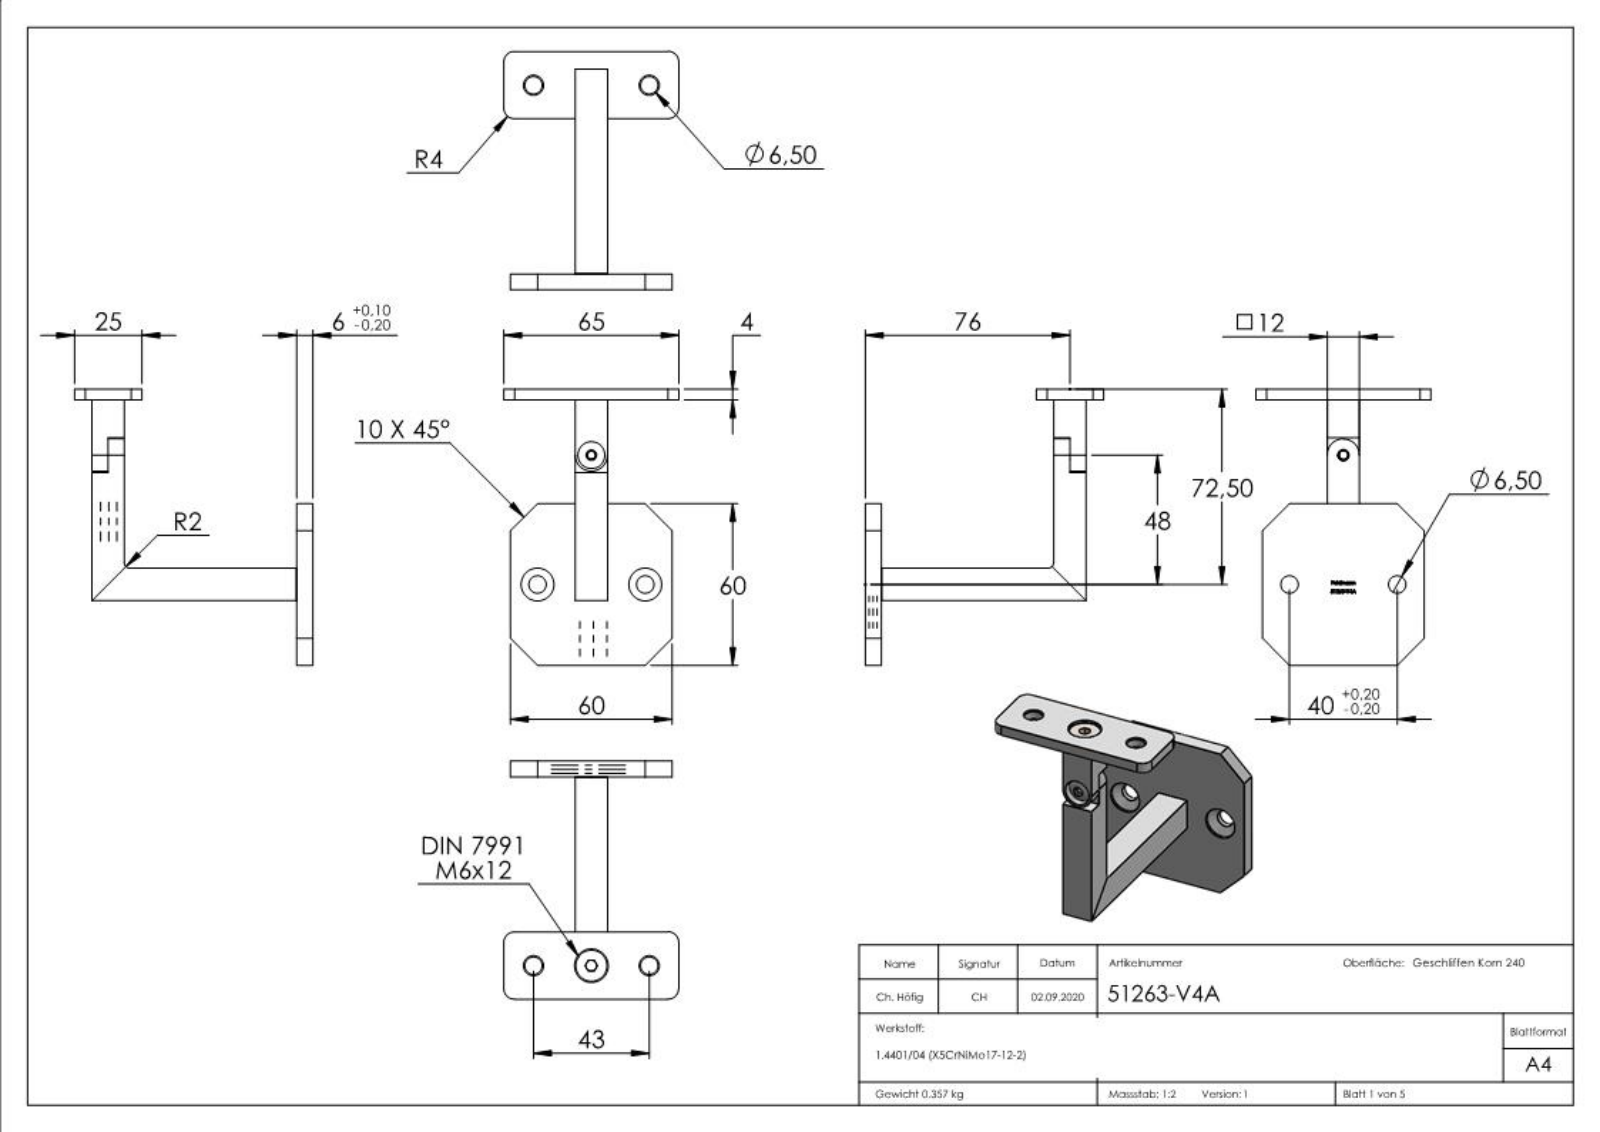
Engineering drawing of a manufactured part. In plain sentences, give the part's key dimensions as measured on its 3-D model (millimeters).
The part is named "5126X-XXX Teil2_5126X-V4A Teil2; socket countersunk head screw_din_DIN 7991 - M6 x 12 --- 12S; 51263-V4A; DIN 7380 M5x8_M5x8 (+7 more)". Its 3-D file was written by "SolidWorks 2018 (CONFIG_CONTROL_DESIGN)". It is 5 solids with 438 faces: 199 planar, 76 cylindrical and 163 other. Overall it measures 102.5 by 88.5 by 65 millimeters. Its volume is 45 039 cubic millimeters and its surface area 20 404 square millimeters. Round holes: 4 of diameter 6.5, 2 of diameter 12.2, 1 of diameter 4.2, 1 of diameter 5, 1 of diameter 5.5, 1 of diameter 7, 1 of diameter 10, 1 of diameter 12.5. Round bosses or shafts: 1 of diameter 12, 1 of diameter 11.57, 1 of diameter 6, 1 of diameter 4.02. Partial cylindrical surfaces (rounded edges, fillets, slot ends): 4 of radius 4, 1 of radius 2. The main face-to-face distances are 6, 12, 4, 78.5, 76, 24, 36, 70, 74.5, 62.5. The hole center spacings are 21.5, 52, 40, 43.
